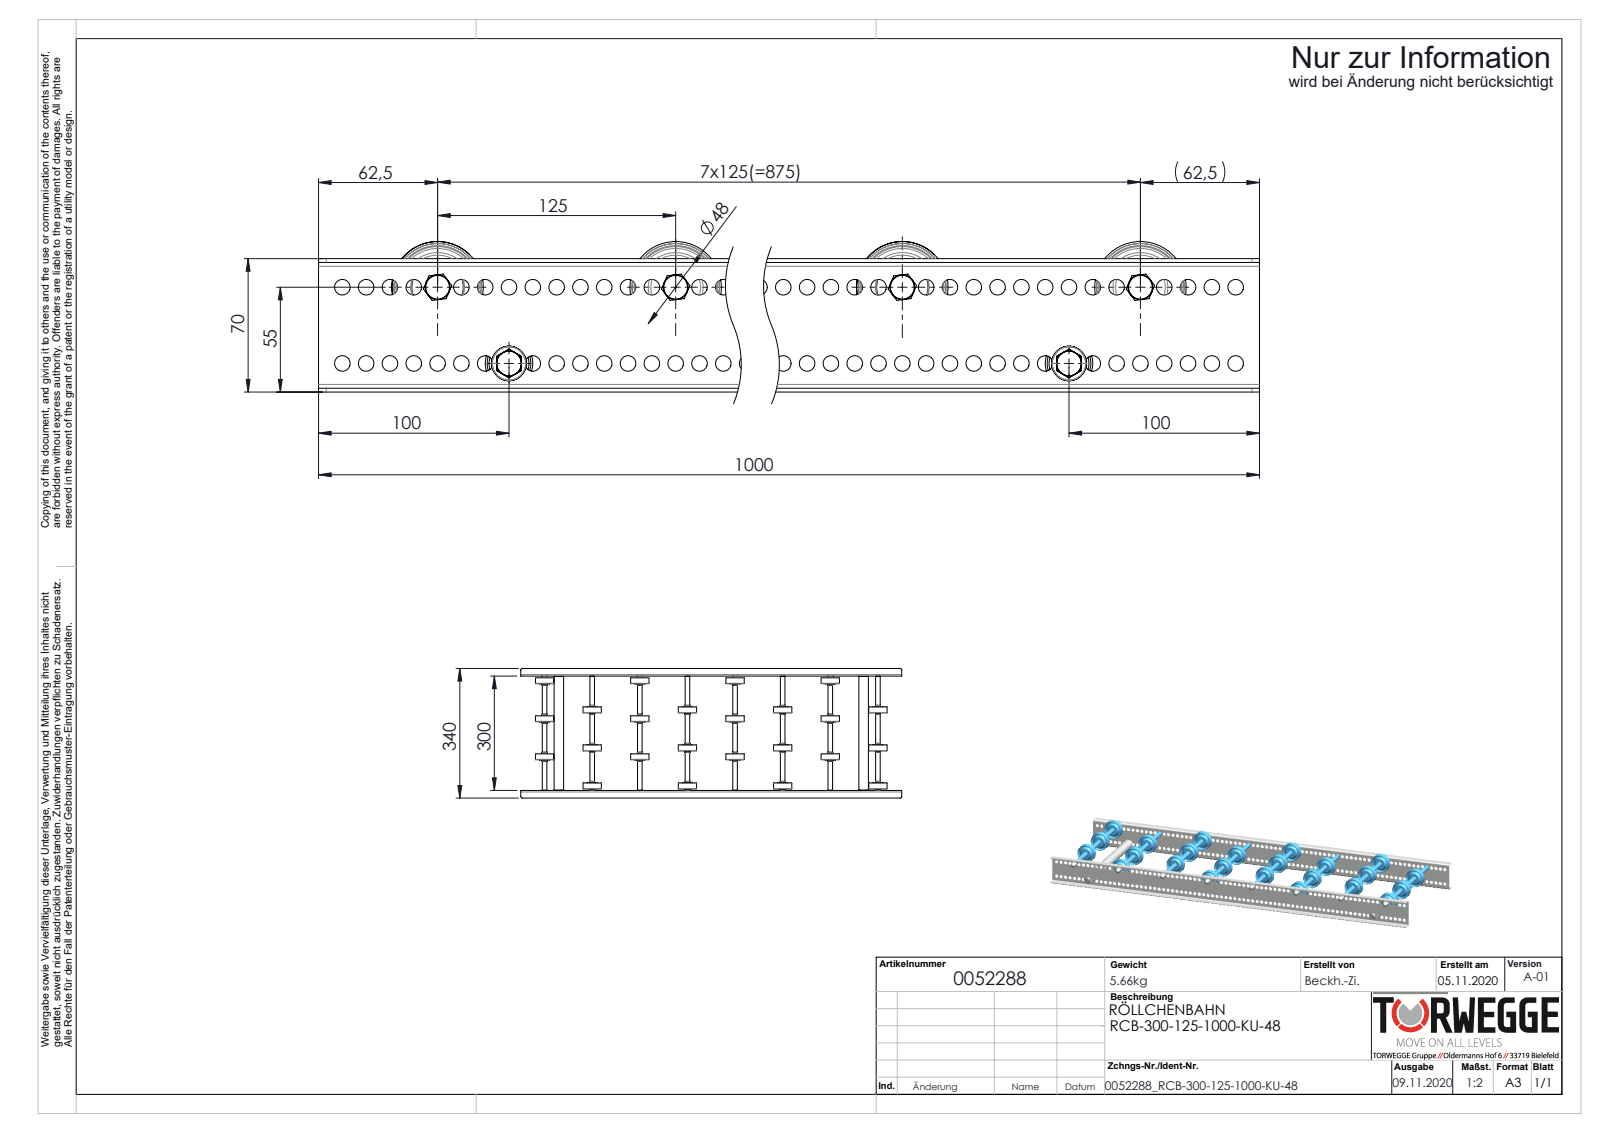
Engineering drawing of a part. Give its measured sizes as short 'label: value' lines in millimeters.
name: Röllchenachse-für-Konfiguration_EL300; S100994_Sperrzahnschraube_M08x16-8.8-A2K; 0052288; Hutmutter_DIN_1587_M8 (+5 more)
written by: SolidWorks 2020 (AUTOMOTIVE_DESIGN)
unit: mm
bodies: 84 solids, 3224 faces (576 planar, 1296 cylindrical, 1352 other)
size: 1000 × 340 × 79
volume: 1 170 000 mm³; area: 939 711 mm²
holes: 158× ⌀8.2, 8× ⌀6.65, 8× ⌀9.65, 8× ⌀13.7, 2× ⌀6.8, 2× ⌀21
bosses: 10× ⌀8, 8× ⌀48, 8× ⌀27, 8× ⌀12.7, 8× ⌀12.5, 8× ⌀12, 2× ⌀25
rounds: 8× R4, 4× R2
face distances: 2, 302, 68, 304, 300, 66, 70, 99.8, 16.3, 76.1
hole spacings: 12.5, 25, 37.5, 50, 62.5, 75, 87.5, 100
